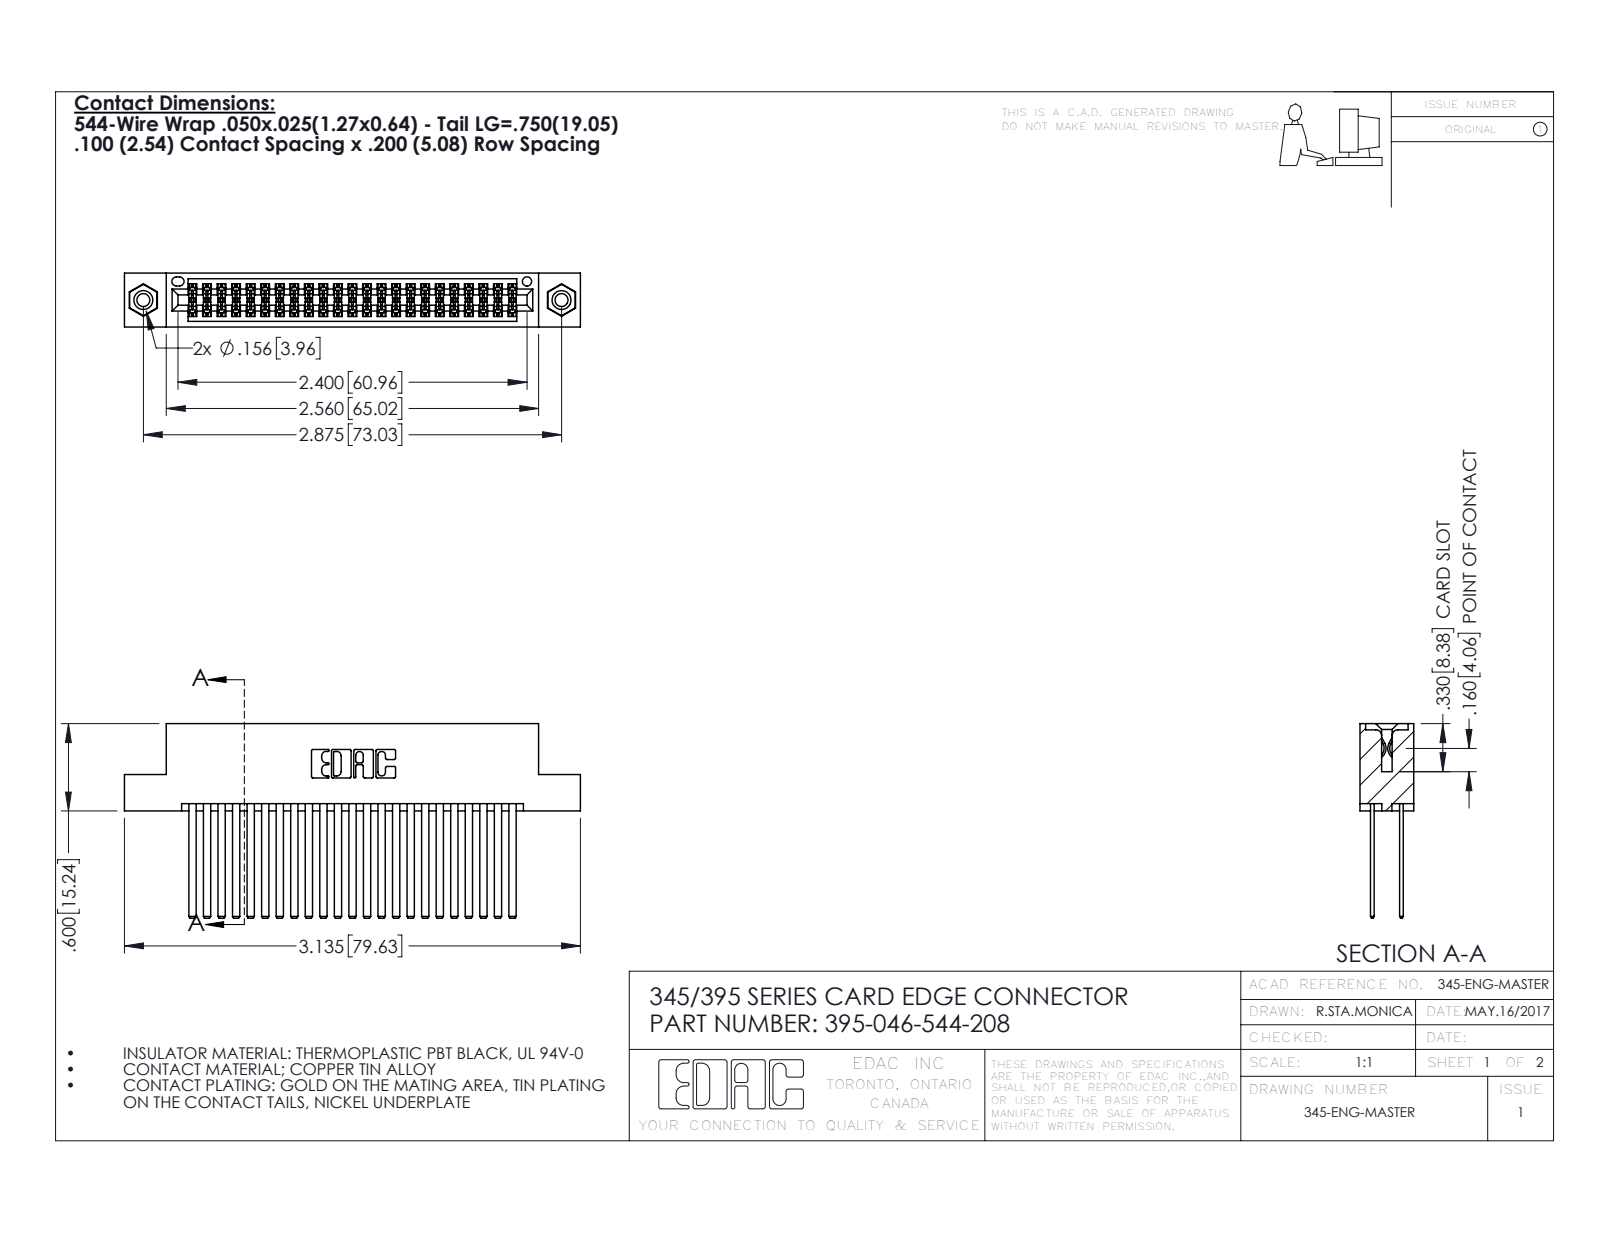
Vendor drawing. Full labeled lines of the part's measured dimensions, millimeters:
Part name (STEP PRODUCT): 345-292-001_345-293-144; 345 Part_Flush Mounting Lugs - 0.156 Dia-TI; 395-046-544-208; 345-250-001_345-250-003-102
STEP written by: SolidWorks 2016 (CONFIG_CONTROL_DESIGN)
Units: millimetres
Bodies: 49 solids, 2210 faces (1446 planar, 748 cylindrical, 16 other)
Overall size (bounding box): 79.6 × 34 × 9.4
Volume: 8 190 mm³ · Surface area: 13 650 mm²
Round holes (diameter × count): ⌀2.3 ×2, ⌀3.2 ×2, ⌀4 ×2, ⌀1.6 ×1
Round bosses / shafts (diameter × count): ⌀3.9 ×2
Partial cylindrical surfaces — rounded edges, fillets, slot ends (radius × count): R0.2 ×69, R0.3 ×22, R0.2 ×6, R0.8 ×6, R0.7 ×3, R0.4 ×2, R0.5 ×2, R0.6 ×2
Main face-to-face distances: 5.1, 1.8, 7.6, 2.5, 6.9, 0.6, 5.7, 9.4, 4.4, 1.3
Hole centre spacings: 6.9, 67.1, 73
